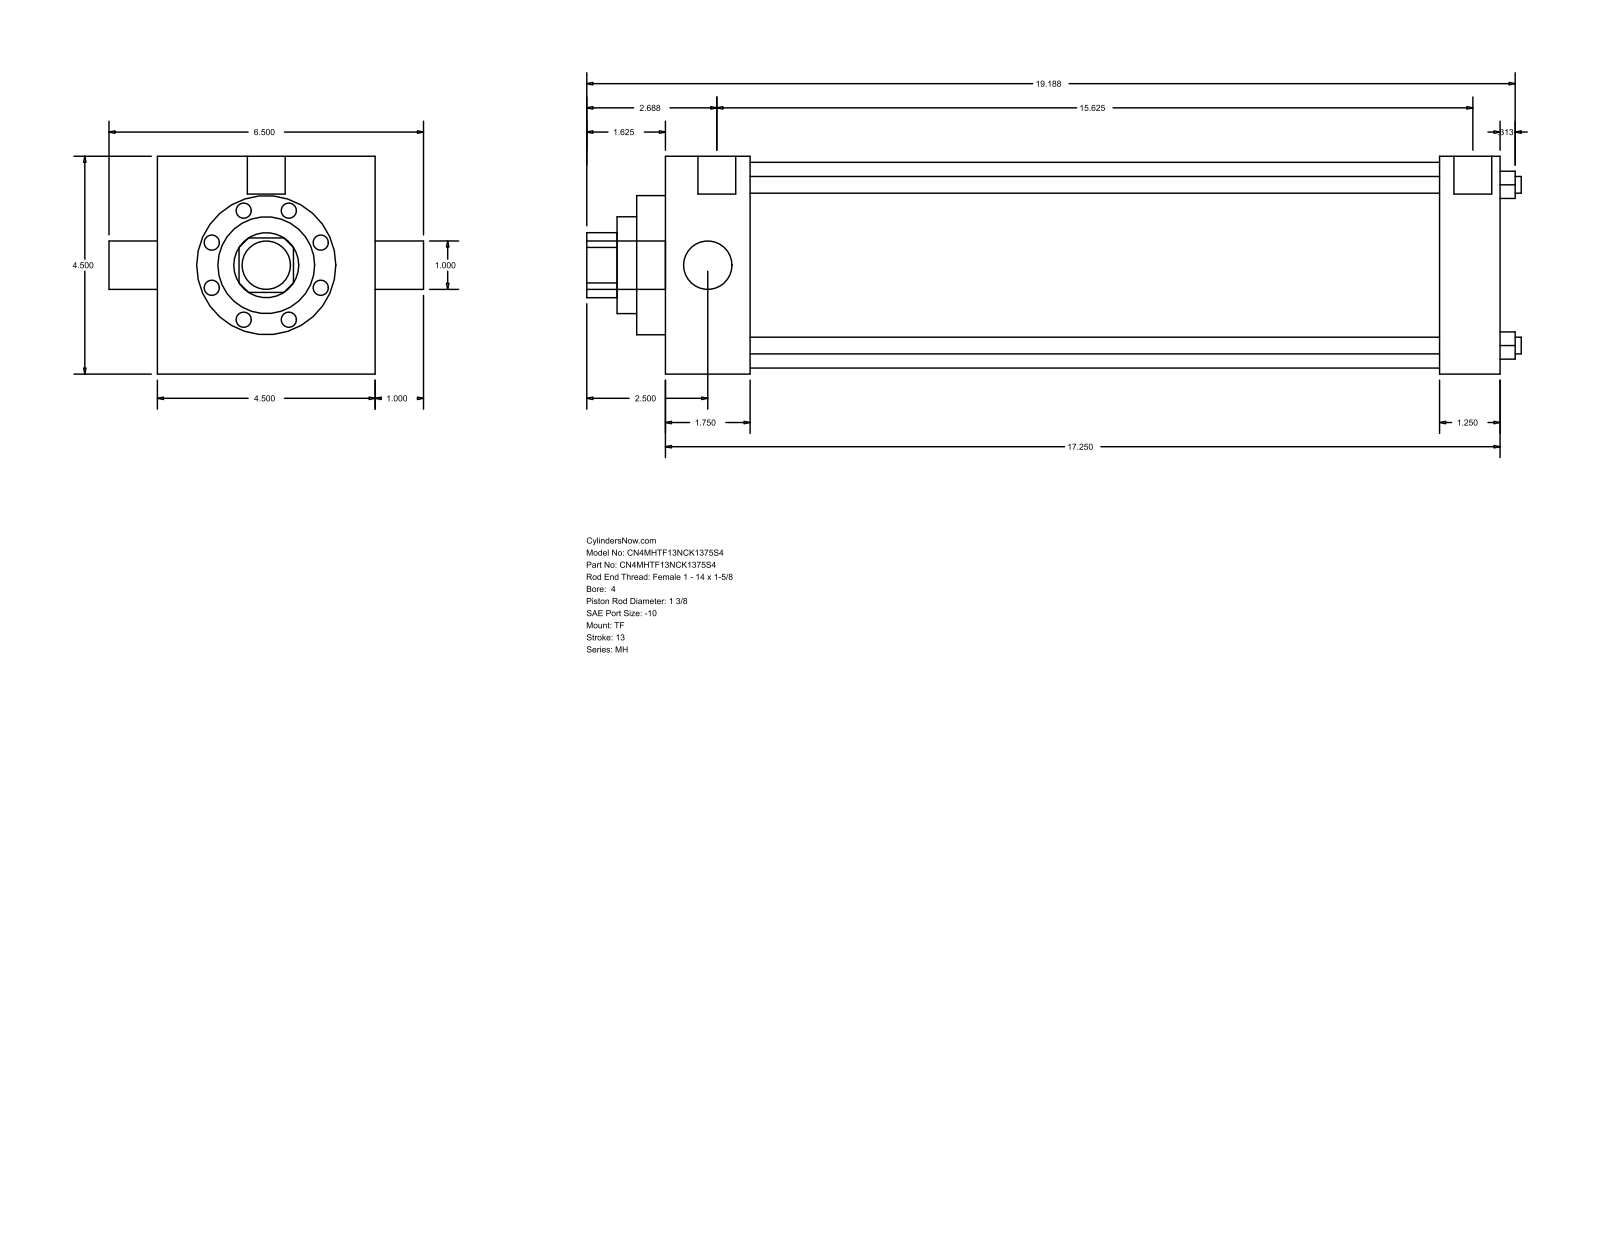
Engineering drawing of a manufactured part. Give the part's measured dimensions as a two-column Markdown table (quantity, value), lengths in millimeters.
| quantity | value |
| --- | --- |
| part name | MH_TF__0400_1.375 |
| STEP written by | GSSL Pune (CONFIG_CONTROL_DESIGN) |
| units | millimeters |
| bodies | 0 solids, 86 faces (61 planar, 25 cylindrical, 0 other) |
| overall size | 490.54 × 165.1 × 114.3 |
| round holes (diameter × count) | 8.76 × 4, 25.4 × 1, 34.92 × 1, 50.8 × 1, 73.03 × 1, 107.95 × 1 |
| round bosses / shafts (diameter × count) | 8.73 × 3, 19.84 × 2, 25.4 × 1 |
| partial cylindrical surfaces (radius × count) | 17.06 × 1 |
| main face-to-face distances | 114.3, 438.16, 44.45, 393.71, 406.41, 361.96, 31.75, 15.08, 59.53, 421.49 |
| hole center spacings | 59.62, 84.32, 119.25 |
